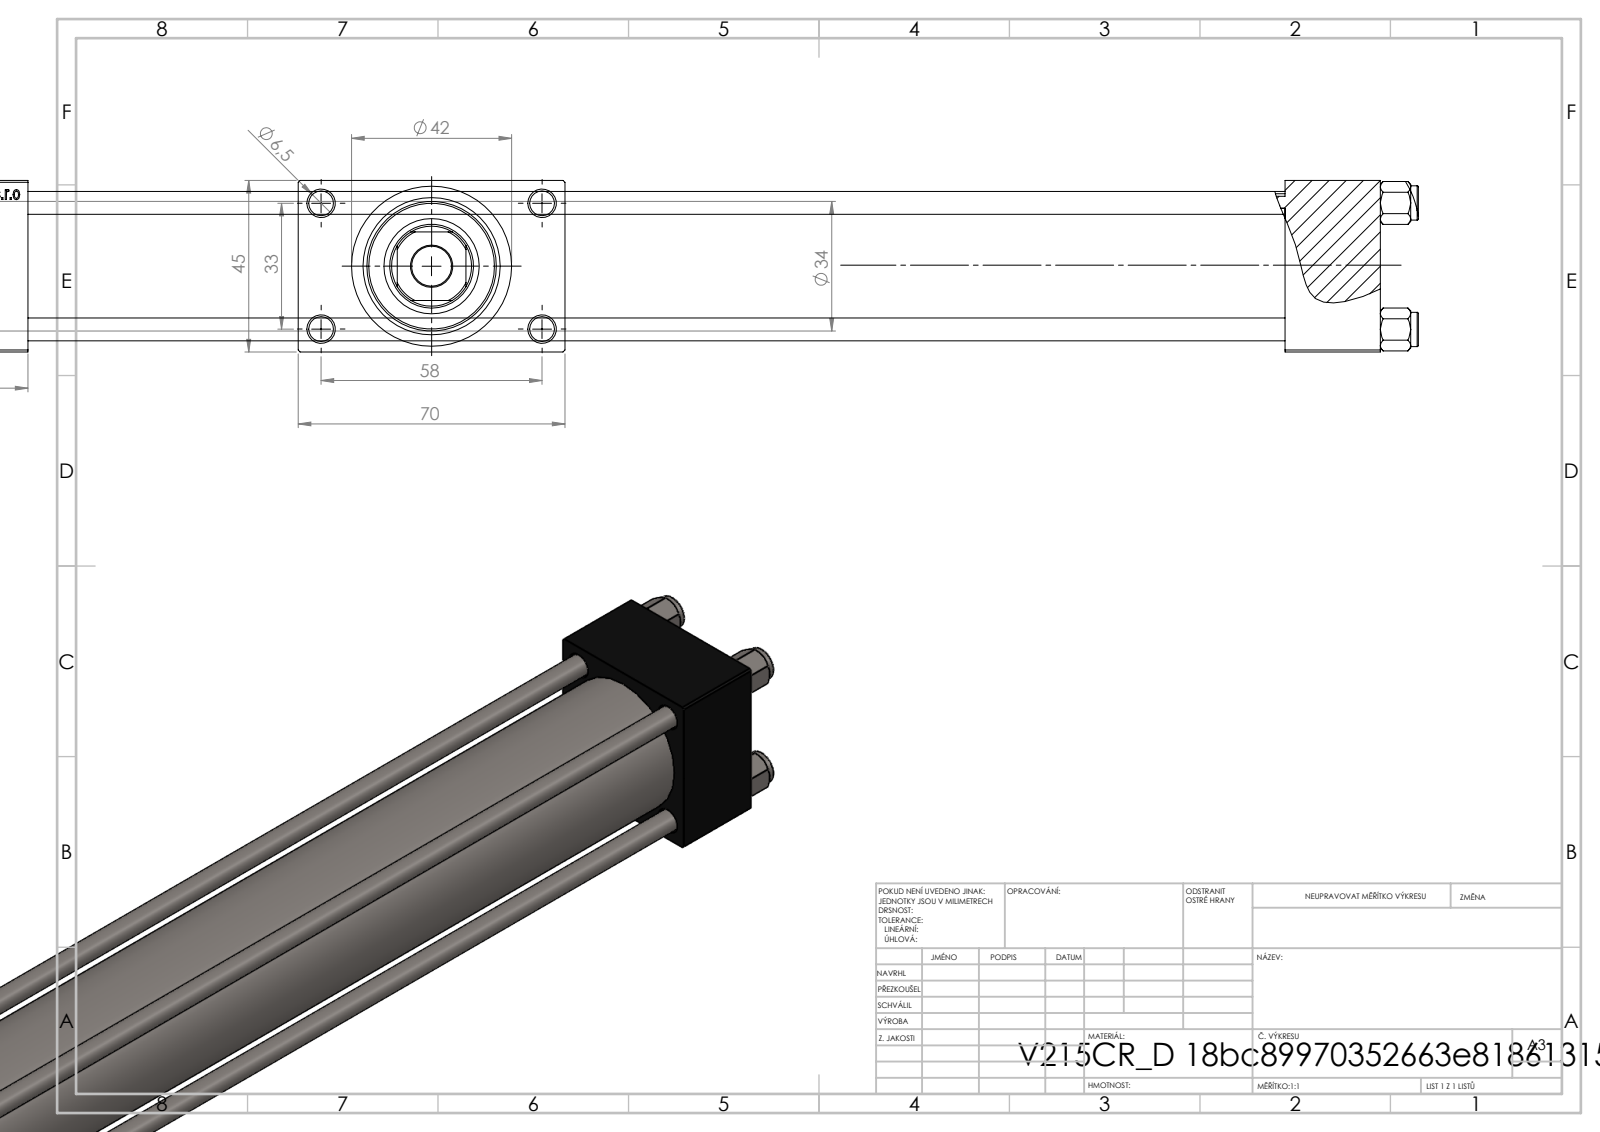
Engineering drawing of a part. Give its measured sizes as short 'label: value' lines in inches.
name: V215CR_VCP_D; NUT_M5_D; V215_VC_A; V215CR_D_Body (+1 more)
written by: SolidWorks 2019 (CONFIG_CONTROL_DESIGN)
unit: in
bodies: 11 solids, 1104 faces (496 planar, 88 cylindrical, 520 other)
size: 17.244 × 2.756 × 1.772
volume: 28.89 in³; area: 282 in²
holes: 4× ⌀0.236, 4× ⌀0.256, 2× ⌀0.276, 2× ⌀0.518, 2× ⌀0.787, 1× ⌀0.413, 1× ⌀0.866, 1× ⌀0.945, 1× ⌀0.984, 1× ⌀1.26, 1× ⌀1.299
bosses: 4× ⌀0.354, 1× ⌀1.654, 1× ⌀1.496, 1× ⌀1.339
rounds: 1× R0.413
face distances: 1.772, 0.984, 0.492, 12.992, 13.976, 2.264, 14.488, 1.496, 15.472, 2.756
hole spacings: 0.488, 0.924, 1.307, 1.314, 1.392, 1.795, 2.219, 1.299
